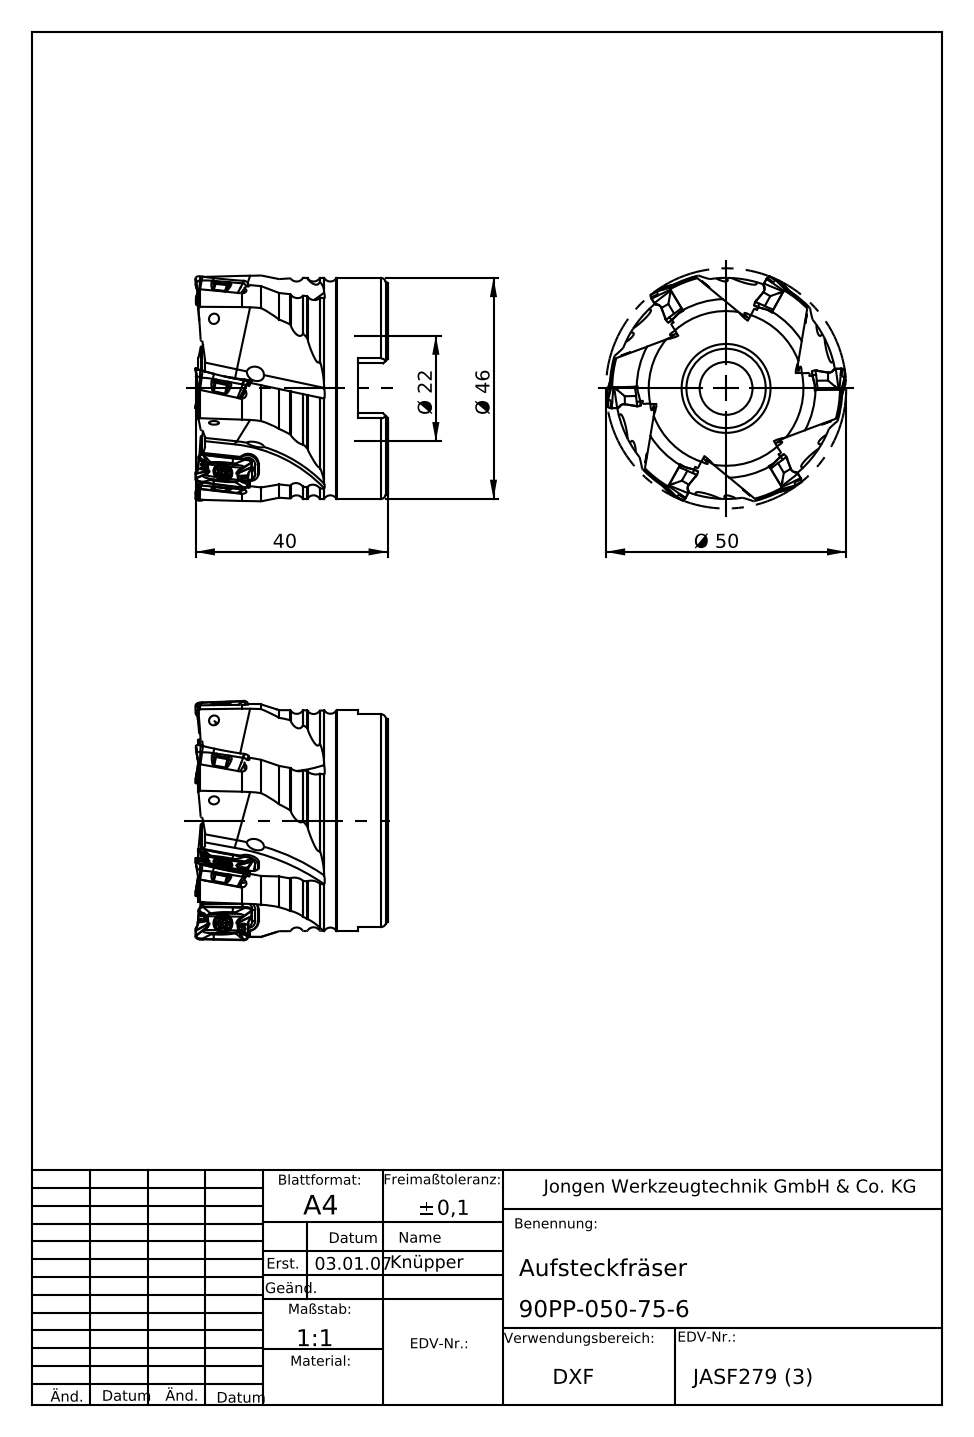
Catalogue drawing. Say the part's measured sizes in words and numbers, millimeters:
The part is named "90PP-050-75-6". Its 3-D file was written by "SolidWorks 2012 (AUTOMOTIVE_DESIGN)". It is 1 solid with 326 faces: 90 planar, 91 cylindrical and 145 other. Overall it measures 50 by 50 by 40 millimeters. Its volume is 48 148 cubic millimeters and its surface area 14 795 square millimeters. Round holes: 6 of diameter 3, 1 of diameter 11, 1 of diameter 16.5, 1 of diameter 22, 1 of diameter 22.15, 1 of diameter 22.3. Round bosses or shafts: 1 of diameter 50, 1 of diameter 46. Partial cylindrical surfaces (rounded edges, fillets, slot ends): 12 of radius 1.5, 12 of radius 2.1, 6 of radius 5, 1 of radius 18.6, 1 of radius 24.19. The main face-to-face distances are 38, 6.3, 31.7, 23, 16.7, 15, 40, 33.7, 17, 2.
